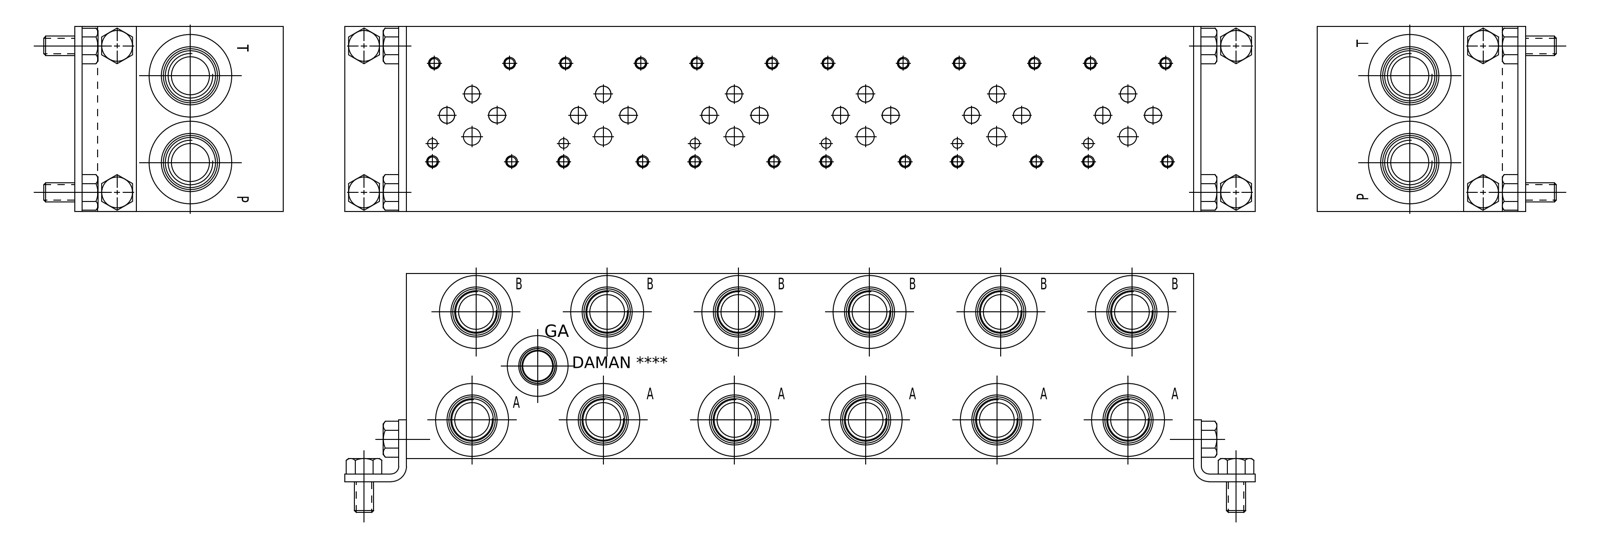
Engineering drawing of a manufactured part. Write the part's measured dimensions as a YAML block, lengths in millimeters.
part_name: "Part_AD03S062S_3D"
step_written_by: "Autodesk Inventor 2020 (AUTOMOTIVE_DESIGN)"
units: millimeters
bodies: {solids: 1, faces: 1017, planar: 479, cylindrical: 174, other: 364}
overall_size: [323.85, 76.2, 76.2]
volume: 1745000
surface_area: 144299
round_holes:
  - {diameter: 3.78, count: 24}
  - {diameter: 4.83, count: 24}
  - {diameter: 6.35, count: 18}
  - {diameter: 14.3, count: 12}
  - {diameter: 17.5, count: 12}
  - {diameter: 19.05, count: 12}
  - {diameter: 19.25, count: 12}
  - {diameter: 30.63, count: 12}
  - {diameter: 3.96, count: 6}
  - {diameter: 7.14, count: 6}
  - {diameter: 6.53, count: 2}
  - {diameter: 7.92, count: 2}
face_to_face_distances: [76.2, 0.79, 75.41, 323.85, 323.06, 322.27, 15.06, 14.27, 61.14, 0.75]
hole_center_spacings: [107.95, 53.97, 53.98, 215.9, 161.92, 161.93, 56.73, 98]
